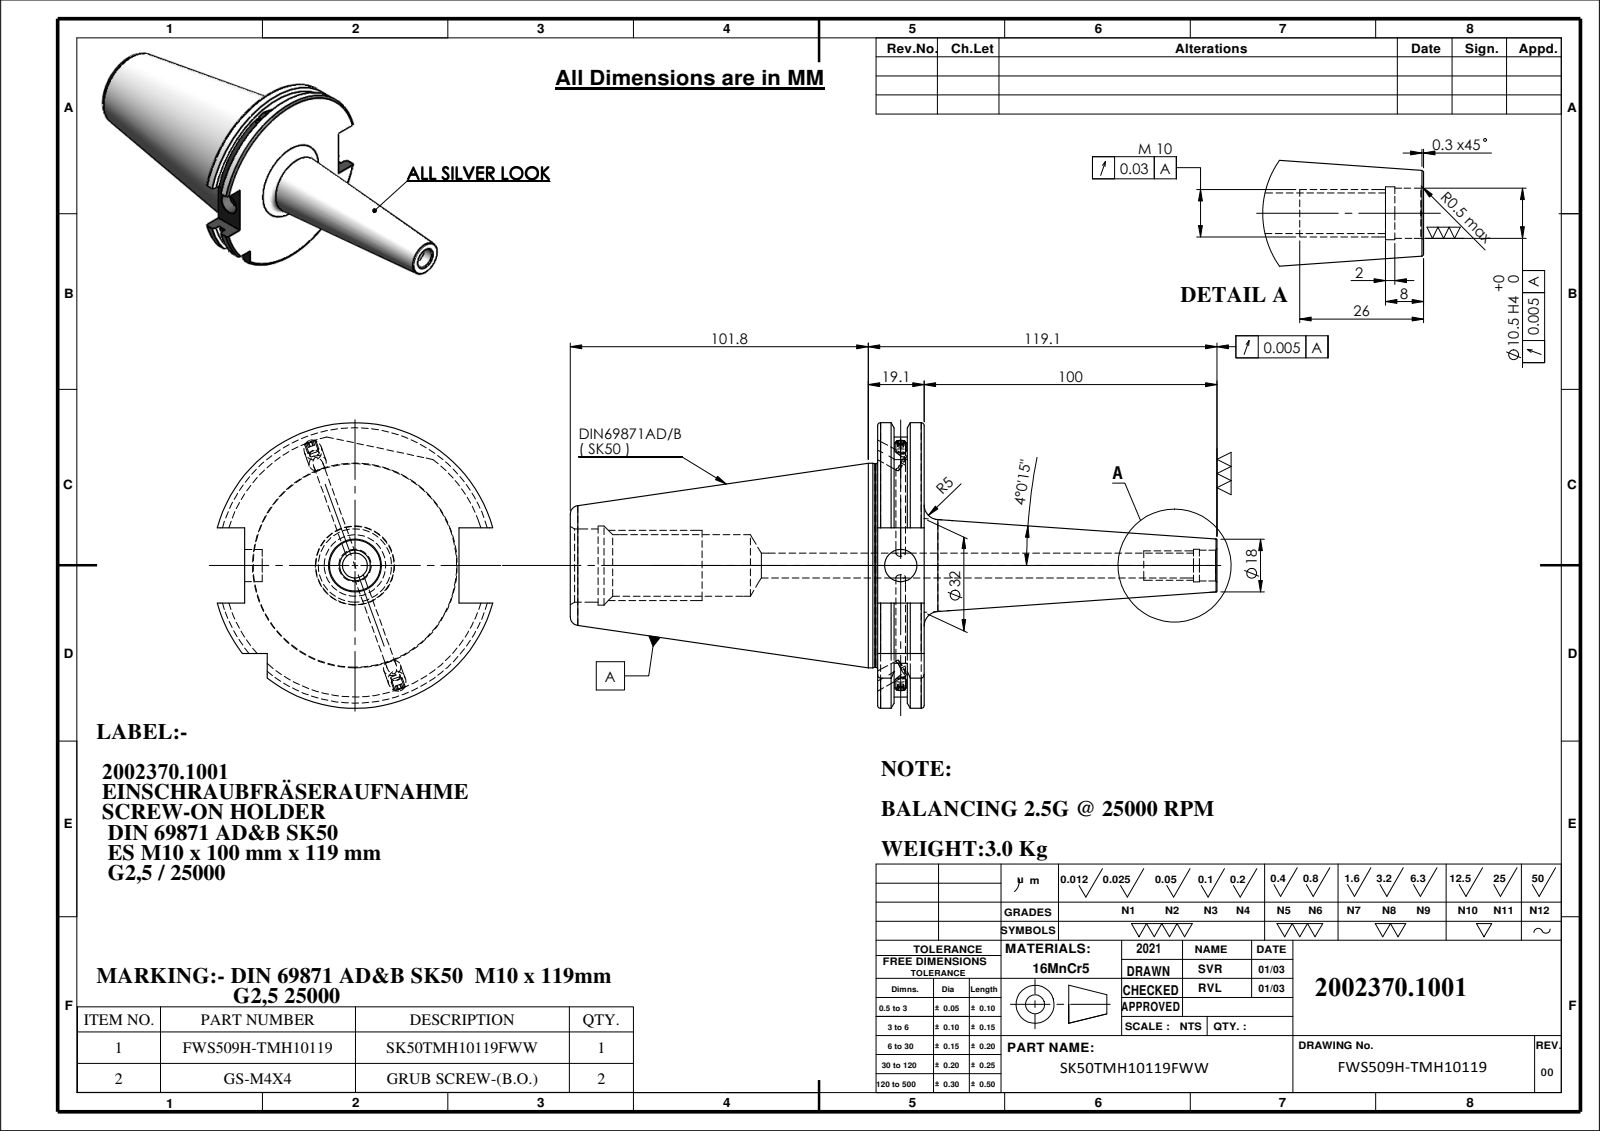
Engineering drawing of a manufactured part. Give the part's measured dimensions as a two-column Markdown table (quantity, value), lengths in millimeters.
| quantity | value |
| --- | --- |
| part name | SK50TMH10119FWW; M4X4_DIN 913 - M4 x 4-N; 91506-ES7M10100 |
| STEP written by | SolidWorks 2018 (AUTOMOTIVE_DESIGN) |
| units | millimeters |
| bodies | 3 solids, 138 faces (43 planar, 47 cylindrical, 48 other) |
| overall size | 220.85 × 97.5 × 94.05 |
| volume | 379 318 mm³ |
| surface area | 53 186 mm² |
| round holes (diameter × count) | 6 × 2, 3.3 × 1, 8.5 × 1, 10.5 × 1, 11 × 1, 11.1 × 1, 21 × 1, 25 × 1, 27 × 1 |
| round bosses / shafts (diameter × count) | 4 × 2, 69.85 × 1, 69.45 × 1 |
| partial cylindrical surfaces (radius × count) | 44.9 × 1, 48.75 × 1 |
| main face-to-face distances | 15.9, 5.66, 10.24, 10.14, 4.48, 5.76, 104.95, 110.61, 115.09, 120.85 |
